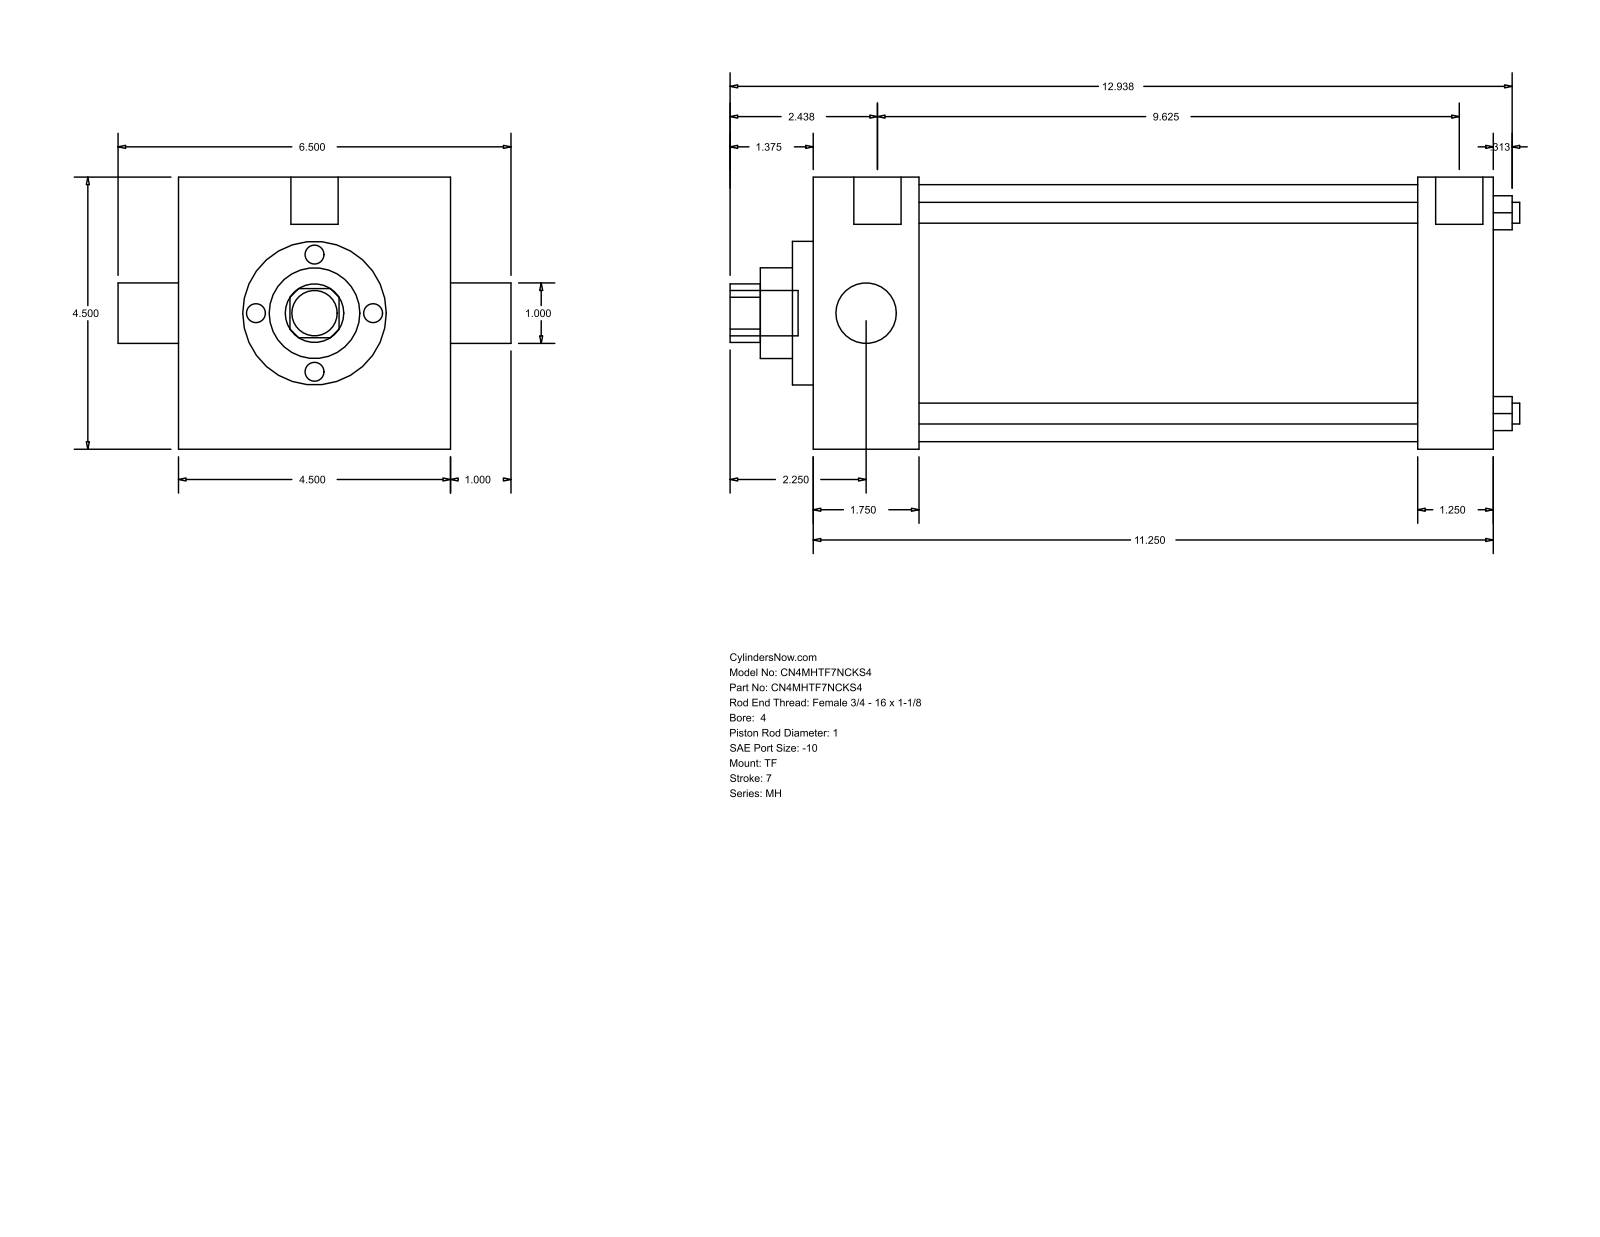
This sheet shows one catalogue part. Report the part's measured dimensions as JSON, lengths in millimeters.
{"part_name": "MH_TF__0400_1", "step_written_by": "GSSL Pune (CONFIG_CONTROL_DESIGN)", "units": "millimeters", "bodies": {"solids": 0, "faces": 86, "planar": 61, "cylindrical": 25, "other": 0}, "overall_size": [331.79, 165.1, 114.3], "round_holes": [[8.76, 4], [25.4, 2], [38.1, 1], [60.33, 1], [107.95, 1]], "round_bosses_or_shafts": [[8.73, 3], [19.84, 2], [19.05, 1]], "partial_cylinders_radius": [[12.29, 1]], "face_to_face_distances": [114.3, 285.76, 44.46, 241.3, 254.01, 209.55, 31.75, 8.73, 53.19, 262.74], "hole_center_spacings": [59.62, 84.32, 119.25]}
